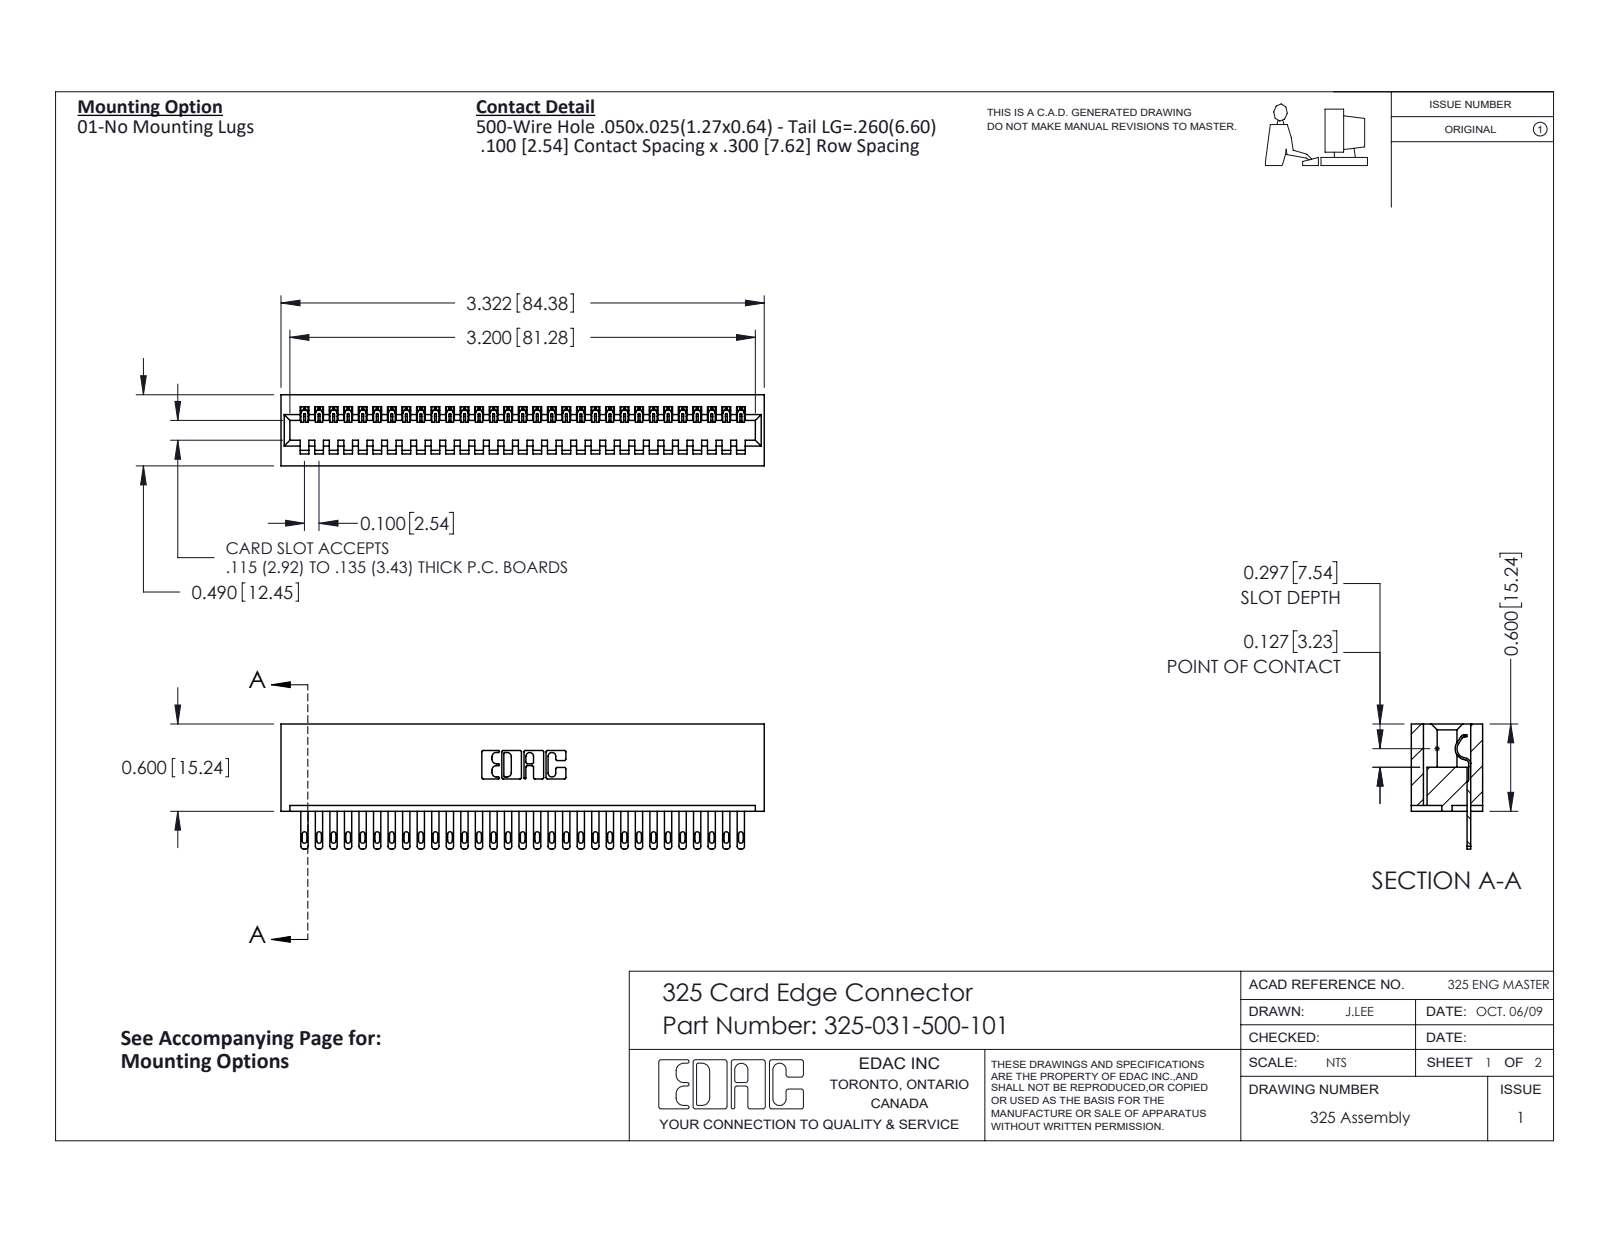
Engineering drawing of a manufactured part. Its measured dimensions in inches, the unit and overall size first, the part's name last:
Units: inches
Overall size (bounding box): 3.322 × 0.86 × 0.49
Partial cylindrical surfaces — rounded edges, fillets, slot ends (radius × count): R0.006 ×62, R0.016 ×62, R0.02 ×62, R0.01 ×22, R0.007 ×6, R0.031 ×6, R0.026 ×3, R0.014 ×1
Main face-to-face distances: 0.083, 0.407, 0.3, 0.49, 0.107, 0.383, 0.025, 0.325, 0.1, 0.2
Volume: 0.684 in³ · Surface area: 19.58 in²
Bodies: 32 solids, 1780 faces (1182 planar, 598 cylindrical, 0 other)
Part name (STEP PRODUCT): 325-031-500-101; 325-292-001_325-293-100; 325 Part_Lugless
STEP written by: SolidWorks 2016 (CONFIG_CONTROL_DESIGN)
